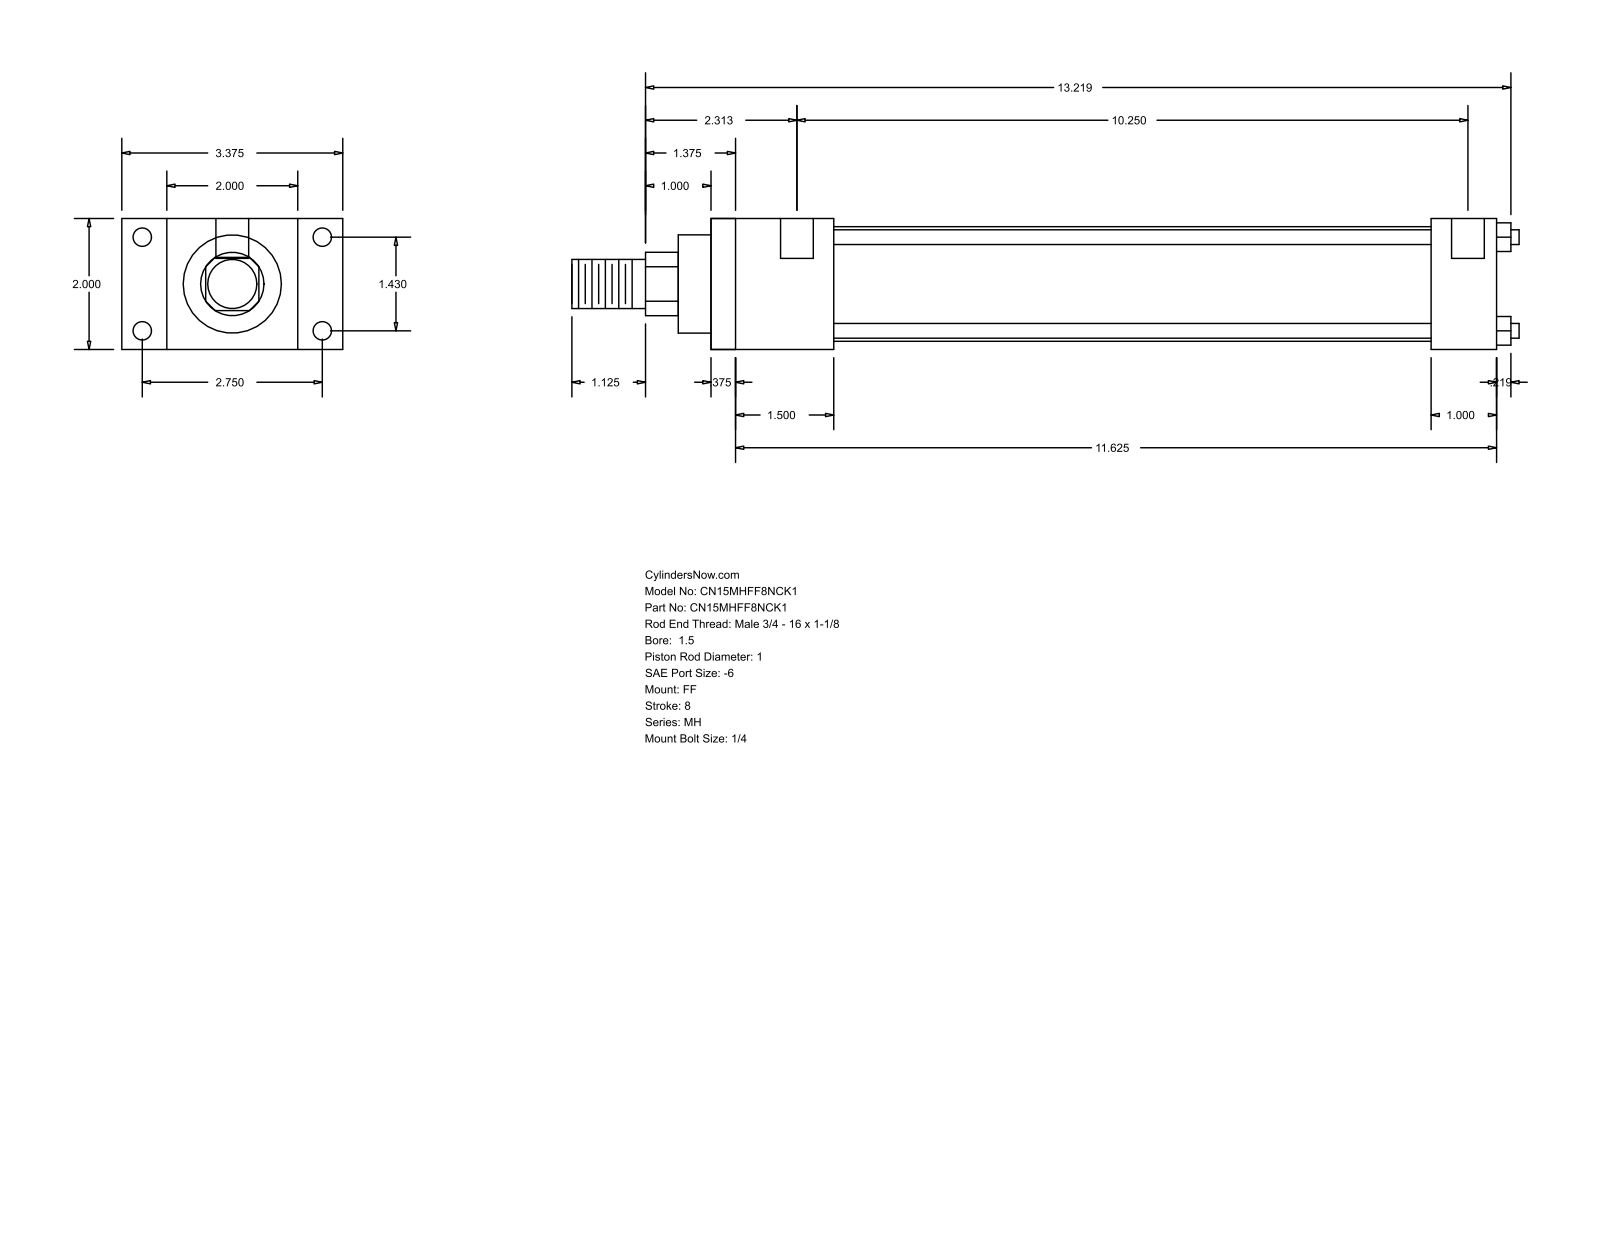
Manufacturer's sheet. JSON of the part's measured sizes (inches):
{"part_name": "MH_FF__0150_1", "step_written_by": "GSSL Pune (CONFIG_CONTROL_DESIGN)", "units": "inches", "bodies": {"solids": 0, "faces": 92, "planar": 64, "cylindrical": 28, "other": 0}, "overall_size": [14.469, 3.375, 2], "round_holes": [[0.219, 4], [0.281, 4], [0.5, 2]], "round_bosses_or_shafts": [[0.225, 4], [1.75, 1], [1.5, 1], [1, 1], [0.75, 1]], "partial_cylinders_radius": [[0.484, 1]], "face_to_face_distances": [2, 12, 0.375, 11.625, 1, 0.687, 2.687, 1.875, 1.5, 10.125], "hole_center_spacings": [1.43, 2.75, 3.099, 10.375, 0.125, 10.25]}
